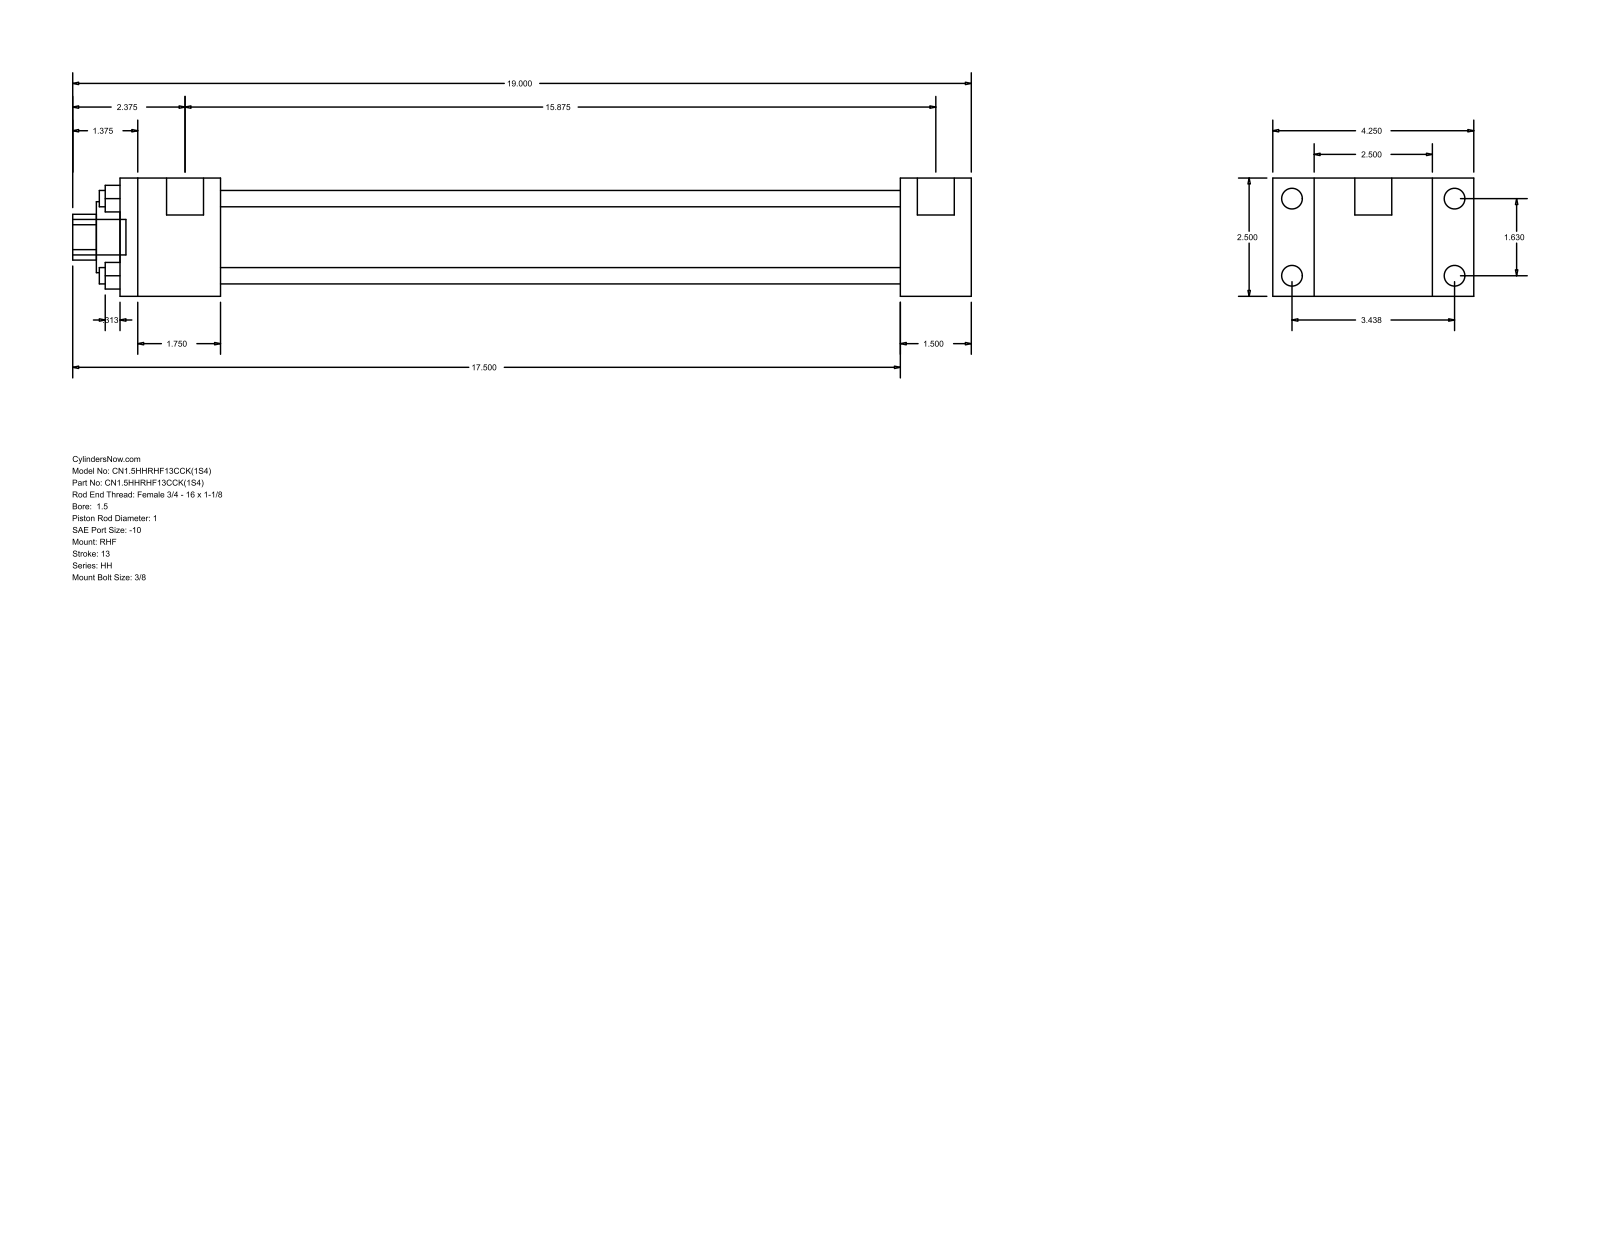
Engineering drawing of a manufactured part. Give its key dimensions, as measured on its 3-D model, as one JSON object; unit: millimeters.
{"part_name": "HH_RHF__0150_1", "step_written_by": "GSSL Pune (CONFIG_CONTROL_DESIGN)", "units": "millimeters", "bodies": {"solids": 0, "faces": 88, "planar": 60, "cylindrical": 28, "other": 0}, "overall_size": [482.6, 107.95, 63.5], "round_holes": [[8.76, 4], [25.4, 1], [38.1, 1], [44.45, 1]], "round_bosses_or_shafts": [[11.13, 4], [5.56, 4], [19.84, 2], [19.05, 1]], "partial_cylinders_radius": [[12.29, 1]], "face_to_face_distances": [63.5, 22.23, 85.73, 38.1, 107.96, 365.12, 403.22, 53.98, 419.1, 457.2], "hole_center_spacings": [29.27, 41.4, 58.55]}
